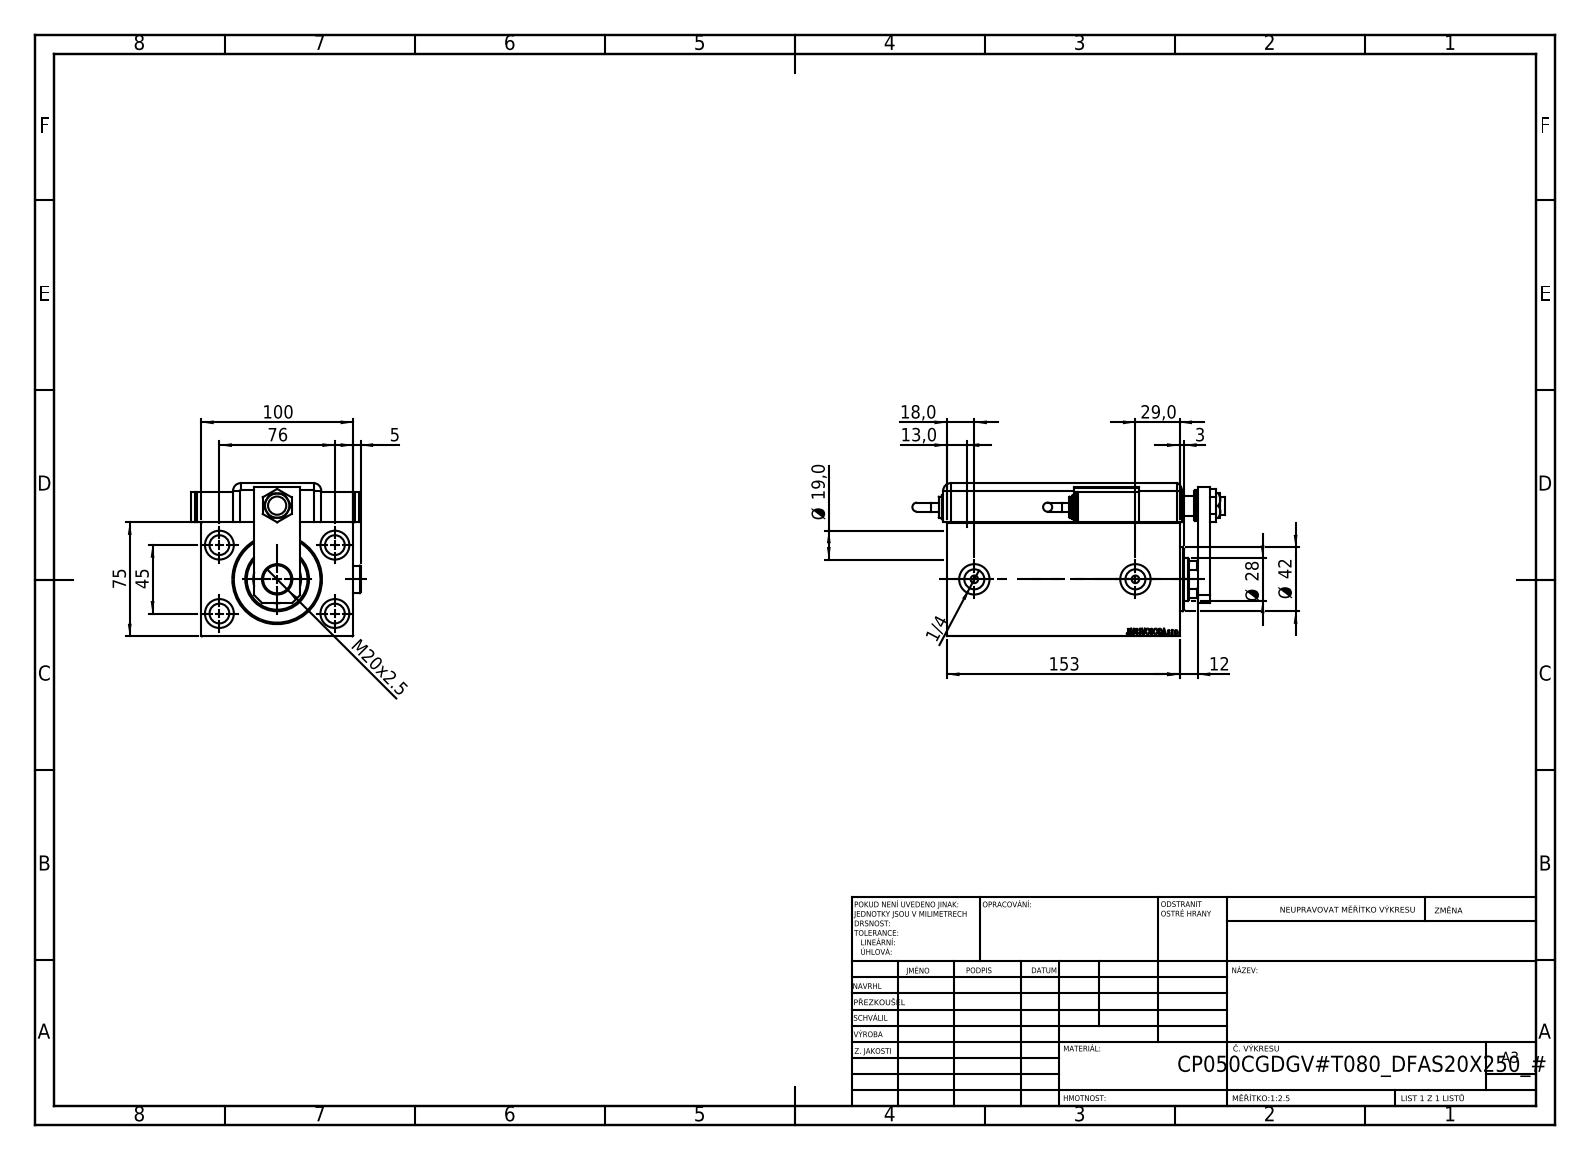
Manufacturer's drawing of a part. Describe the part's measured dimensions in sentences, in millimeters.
The part is named "TYC; KRYT; SWITCH_Q_FRONT_BACK; Zatka_OIL_PORT (+7 more)". Its 3-D file was written by "SolidWorks 2019 (CONFIG_CONTROL_DESIGN)". It is 15 solids with 1303 faces: 649 planar, 133 cylindrical and 521 other. Overall it measures 205.46 by 111.9 by 100.8 millimeters. Its volume is 1 106 000 cubic millimeters and its surface area 218 099 square millimeters. Round holes: 5 of diameter 13, 4 of diameter 19, 3 of diameter 20, 2 of diameter 4, 2 of diameter 5, 2 of diameter 8, 2 of diameter 13.16, 1 of diameter 12, 1 of diameter 14, 1 of diameter 18.5, 1 of diameter 28, 1 of diameter 31.5. Round bosses or shafts: 3 of diameter 20, 2 of diameter 18, 2 of diameter 16, 2 of diameter 14, 2 of diameter 6, 1 of diameter 42. Partial cylindrical surfaces (rounded edges, fillets, slot ends): 9 of radius 5, 1 of radius 10, 1 of radius 13.5. The main face-to-face distances are 75, 3, 100, 25.8, 100.8, 24, 97.8, 22.8, 14, 79. The hole center spacings are 44.16, 45, 46.04, 76, 80.53, 88.32, 20, 48.5.
